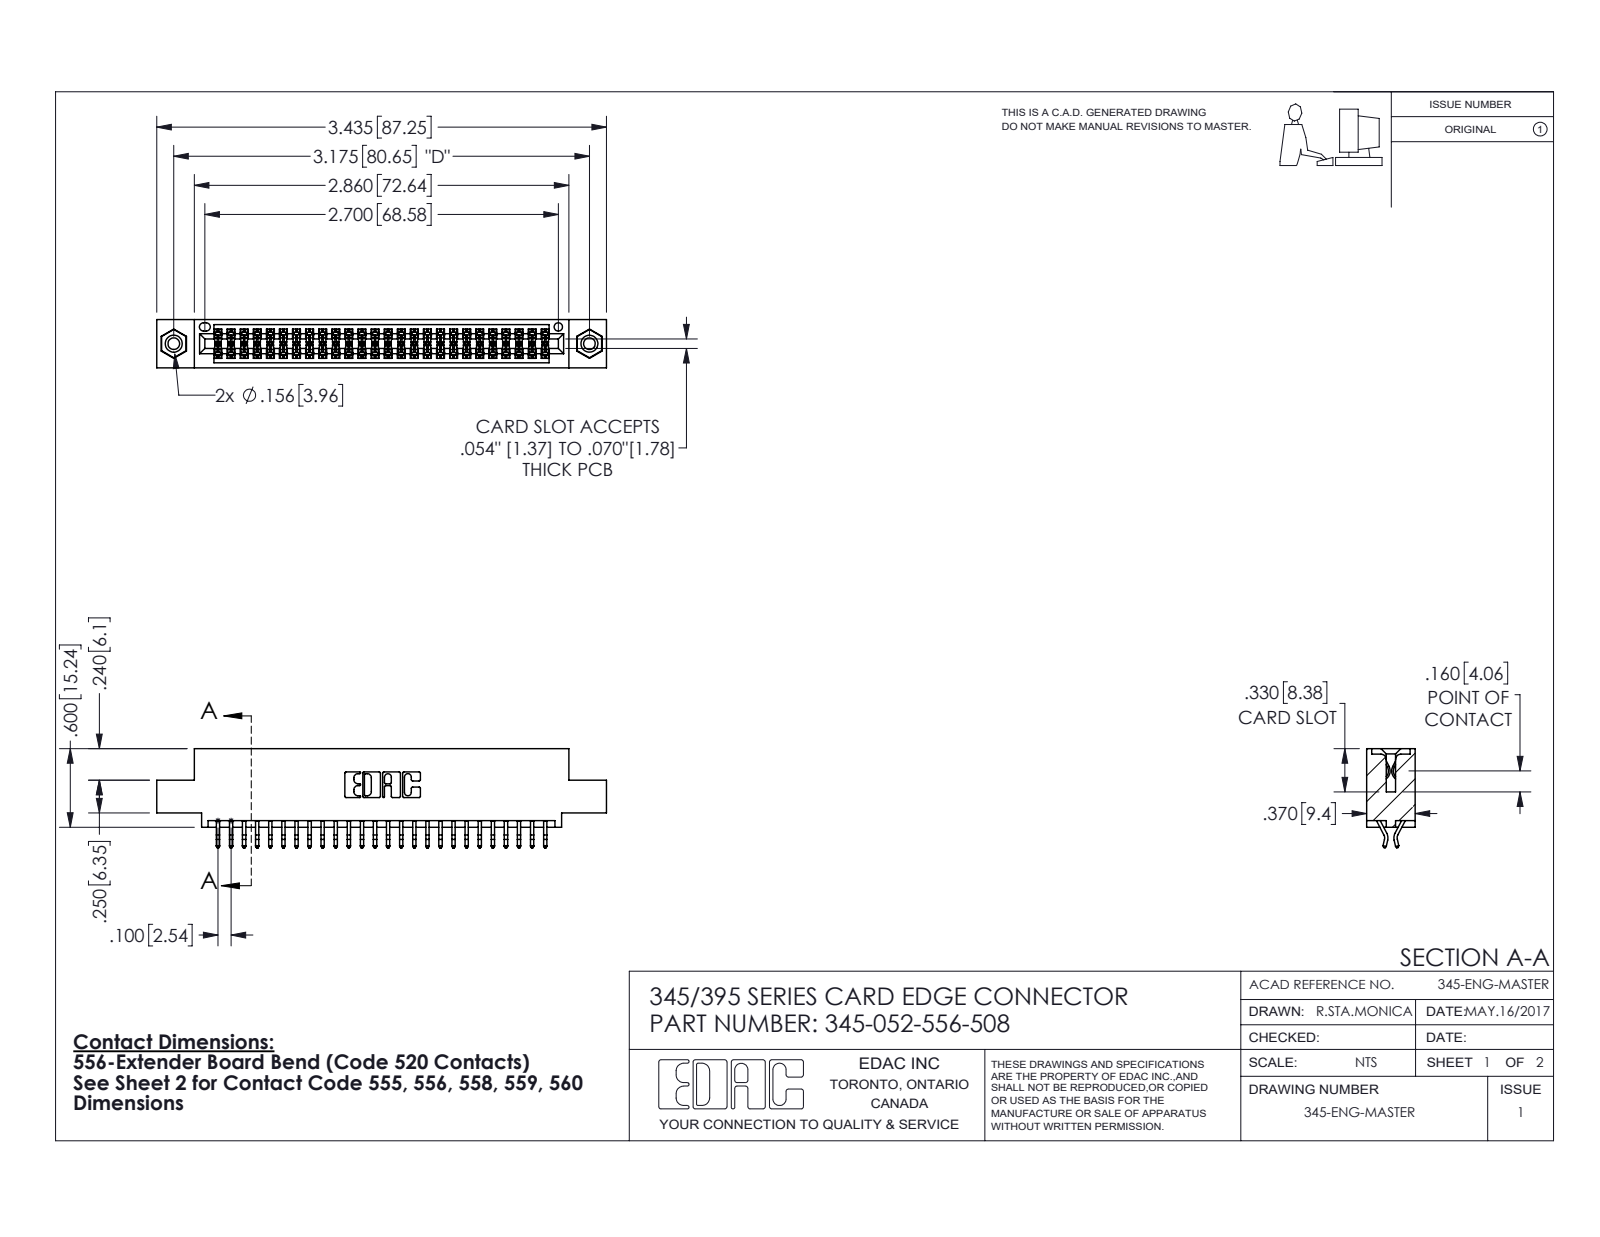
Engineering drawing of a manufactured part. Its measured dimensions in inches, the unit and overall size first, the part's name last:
Units: inches
Overall size (bounding box): 3.435 × 0.757 × 0.37
Round holes (diameter × count): ⌀0.089 ×2, ⌀0.125 ×2, ⌀0.156 ×2, ⌀0.064 ×1
Round bosses / shafts (diameter × count): ⌀0.155 ×2
Partial cylindrical surfaces — rounded edges, fillets, slot ends (radius × count): R0.006 ×78, R0.01 ×22, R0.007 ×6, R0.031 ×6, R0.026 ×3, R0.01 ×2, R0.014 ×2, R0.019 ×2
Main face-to-face distances: 0.072, 0.298, 0.2, 0.37, 0.025, 0.098, 0.272, 0.225, 0.175, 0.149
Hole centre spacings: 0.27, 2.94, 3.175
Volume: 0.503 in³ · Surface area: 18.5 in²
Bodies: 55 solids, 3102 faces (2040 planar, 1046 cylindrical, 16 other)
Part name (STEP PRODUCT): 345 Part_0.110 Offset - 0.156 Dia-TI; 345-292-001_556 Tail; 345-250-001_345-250-003-102; 345-052-556-508
STEP written by: SolidWorks 2016 (CONFIG_CONTROL_DESIGN)
